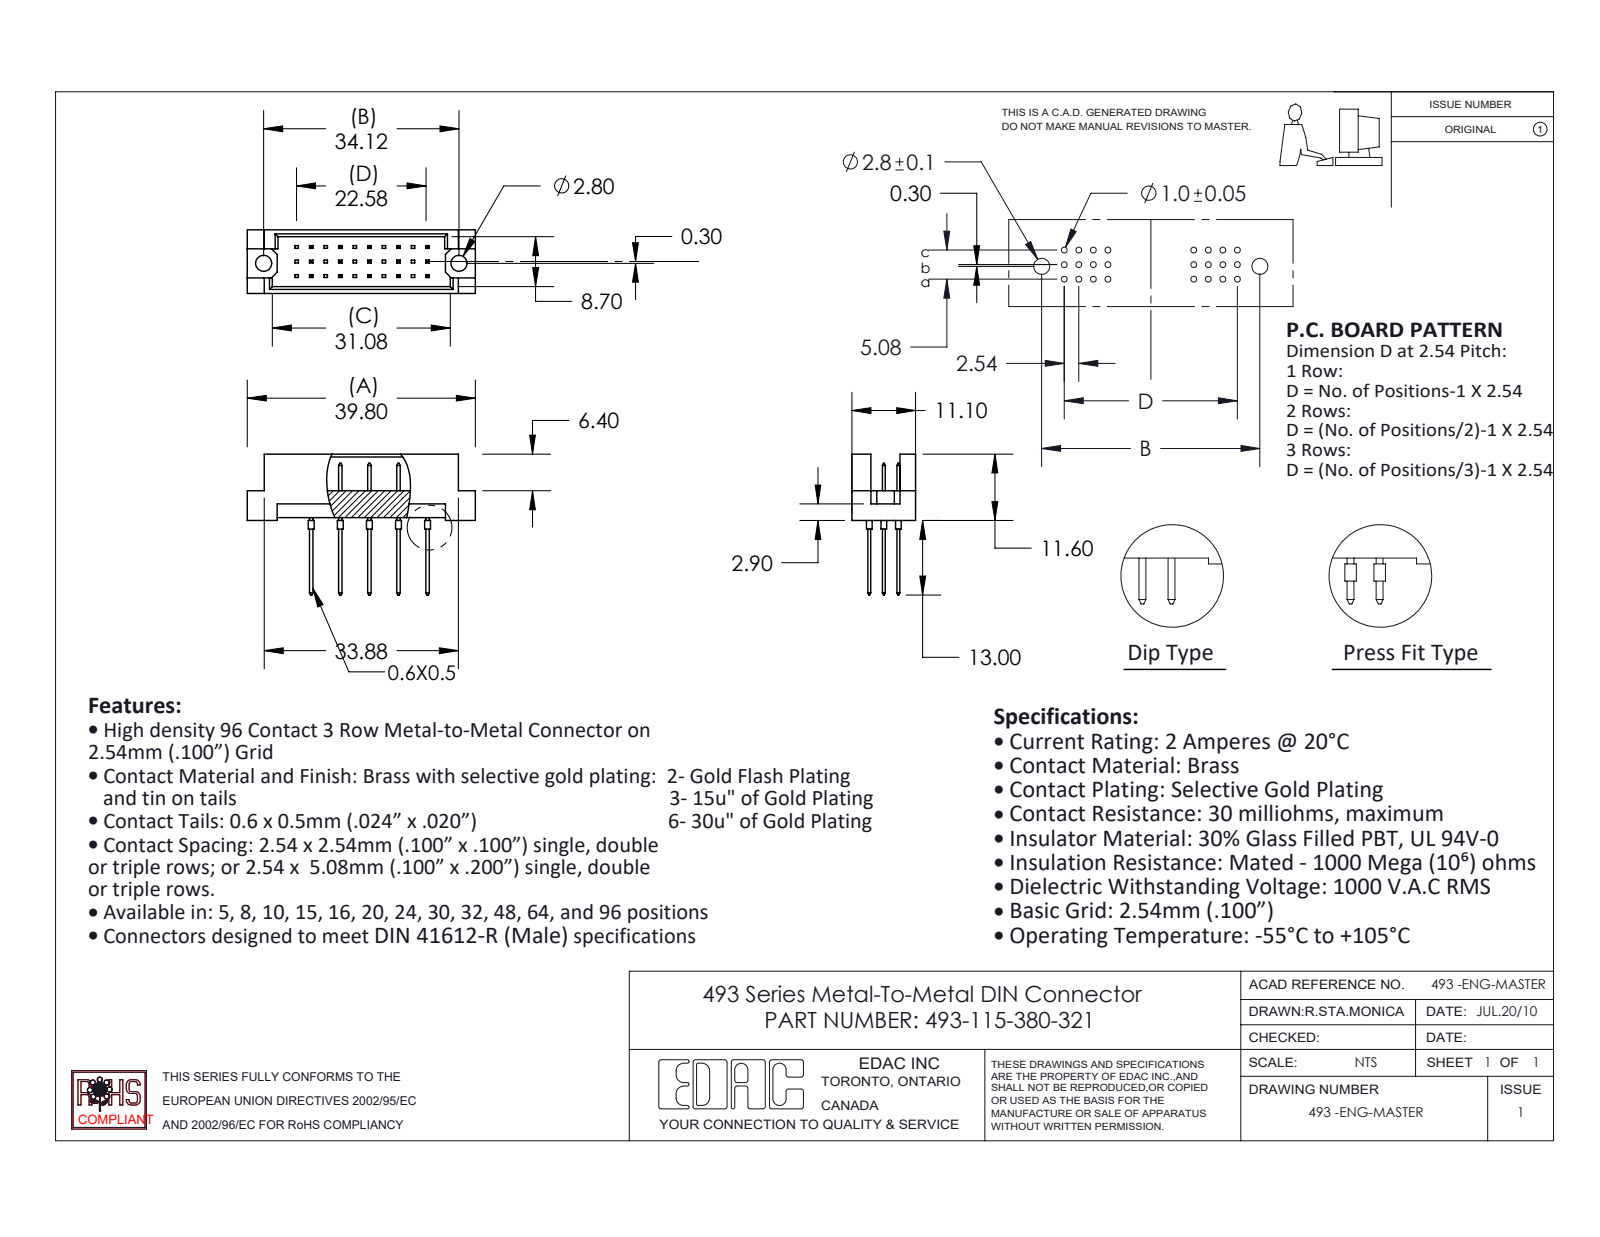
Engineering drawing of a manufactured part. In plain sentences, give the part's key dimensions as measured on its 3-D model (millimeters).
The part is named "493-290_80; 493 Part_30; 493-115-380-322". Its 3-D file was written by "SolidWorks 2020 (CONFIG_CONTROL_DESIGN)". It is 16 solids with 502 faces: 468 planar, 34 cylindrical and 0 other. Overall it measures 39.8 by 24.6 by 11.1 millimeters. Its volume is 2 486 cubic millimeters and its surface area 3 527 square millimeters. Round holes: 2 of diameter 2.8. Round bosses or shafts: 15 of diameter 1. The main face-to-face distances are 5.08, 1.2, 9.9, 11.1, 0.5, 2.54, 8.7, 4.7, 10.16, 0.6. The hole center spacings are 34.12.
